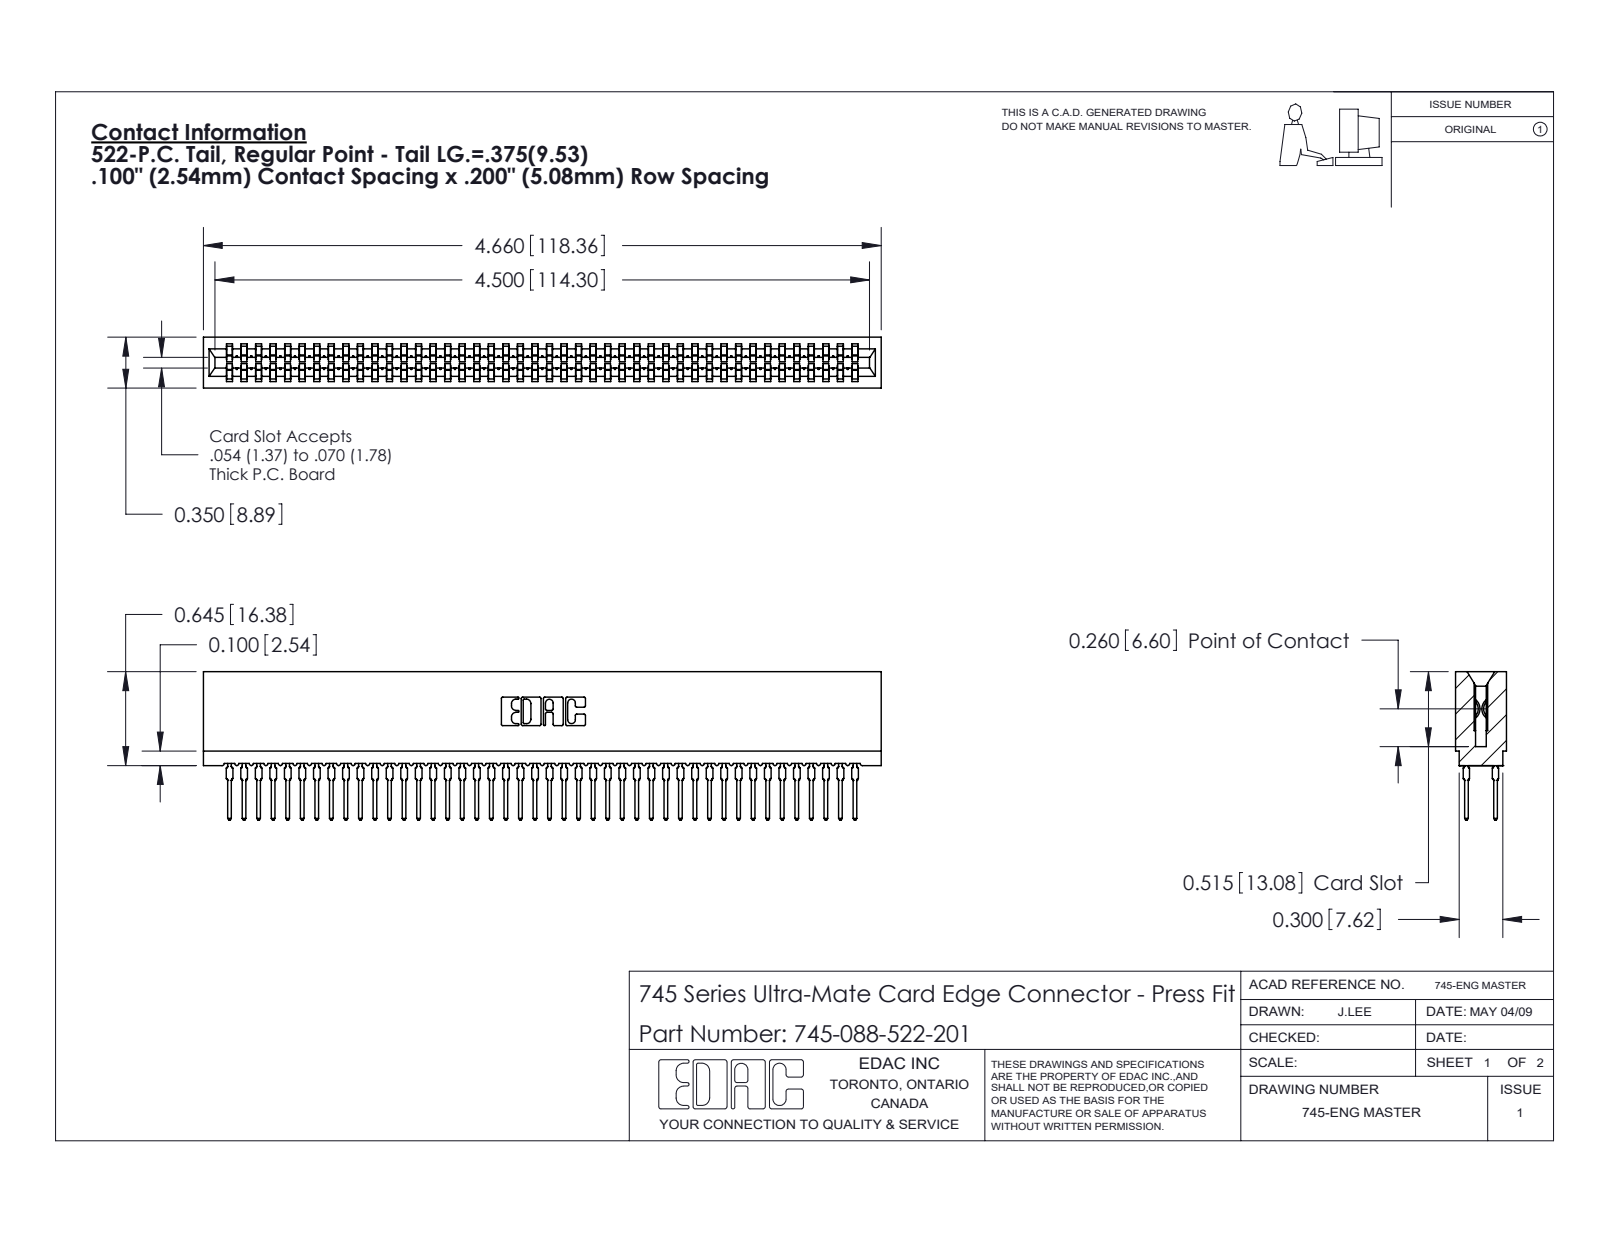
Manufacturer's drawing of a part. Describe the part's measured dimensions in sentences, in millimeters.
The part is named "745-292-001_522; 745-088-522-201; 745 Part_Insulator Option - 01". Its 3-D file was written by "SolidWorks 2020 (CONFIG_CONTROL_DESIGN)". It is 89 solids with 7971 faces: 4103 planar, 1580 cylindrical and 2288 other. Overall it measures 118.4 by 25.9 by 8.9 millimeters. Its volume is 10 700 cubic millimeters and its surface area 22 190 square millimeters. Partial cylindrical surfaces (rounded edges, fillets, slot ends): 176 of radius 0.5, 88 of radius 0.4, 22 of radius 0.3, 8 of radius 0.1, 8 of radius 0.3, 6 of radius 0.2, 6 of radius 0.8, 3 of radius 0.7. The main face-to-face distances are 8.9, 1.6, 7.3, 1.1, 7.7, 0.5, 6.2, 3.5, 5.4, 2.4.
